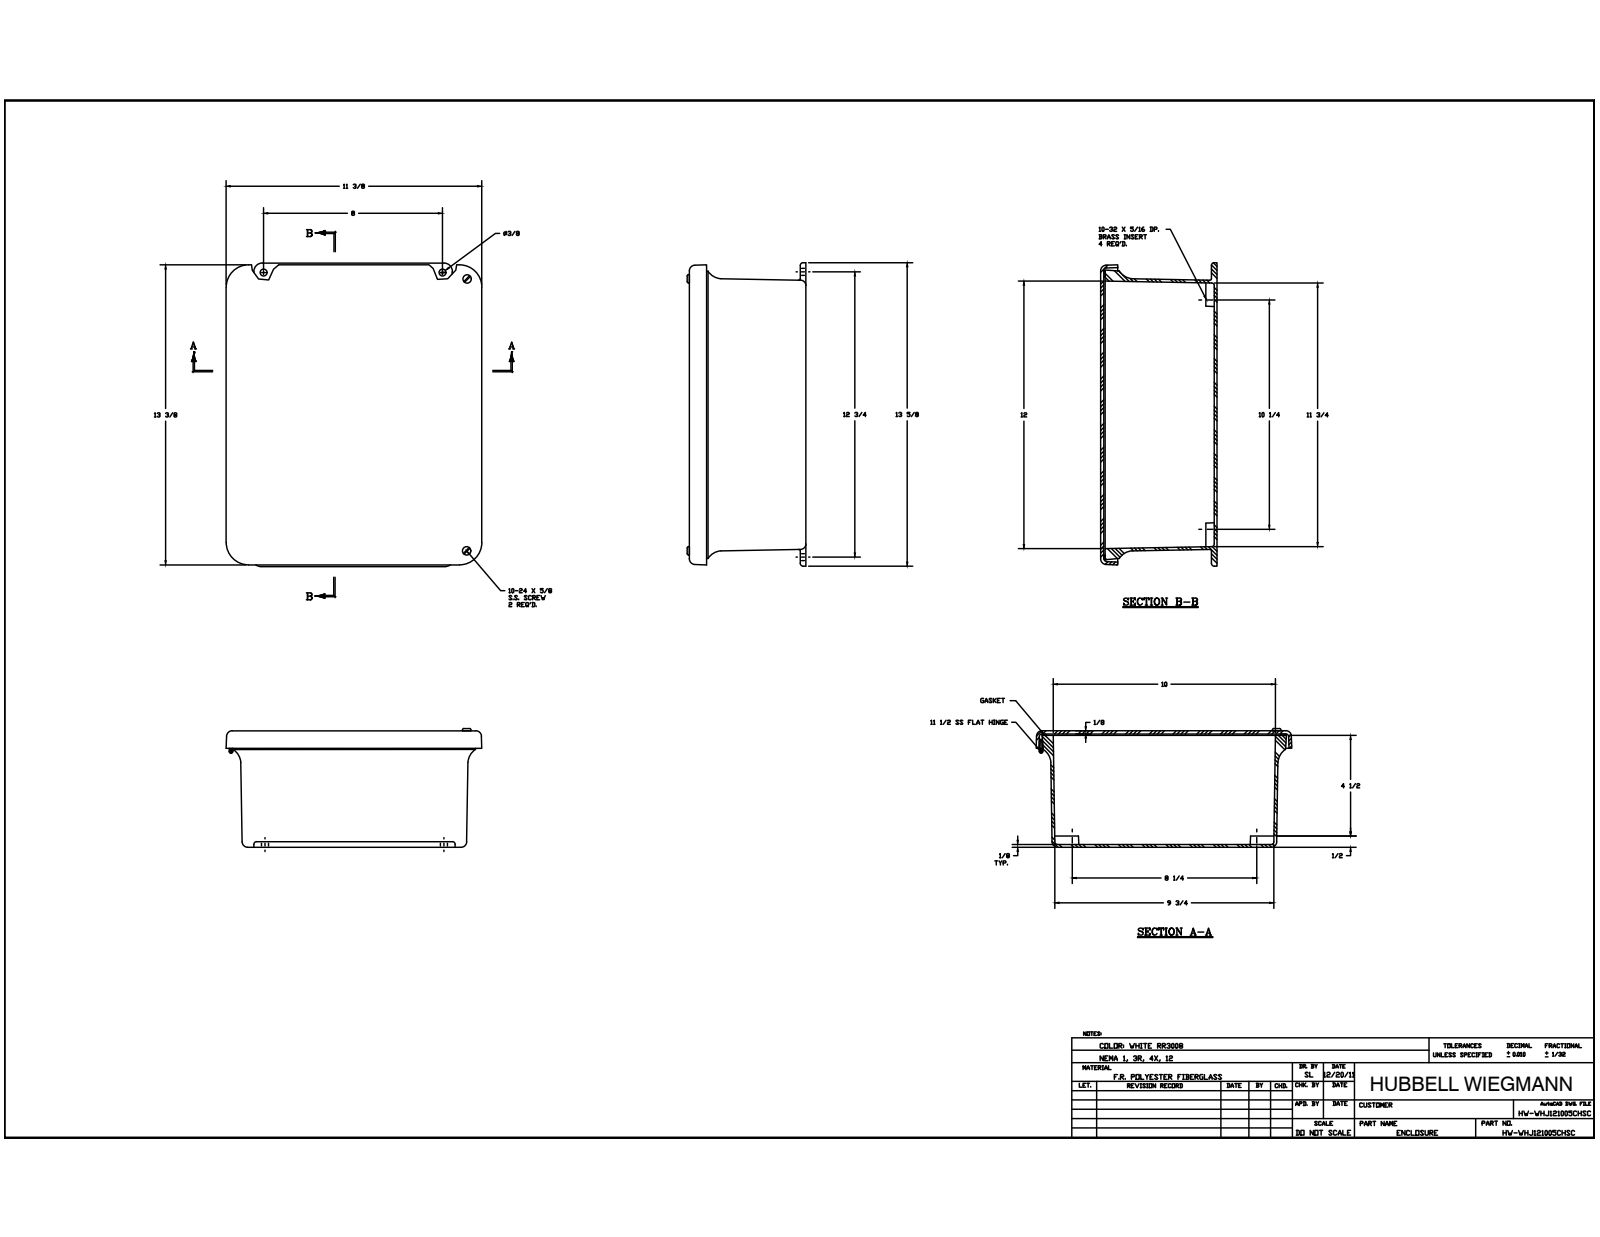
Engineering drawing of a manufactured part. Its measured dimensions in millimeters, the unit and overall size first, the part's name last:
Units: millimetres
Overall size (bounding box): 344.49 × 291.05 × 136.19
Round holes (diameter × count): ⌀3.33 ×8, ⌀3.56 ×8, ⌀3.86 ×5, ⌀3.96 ×4, ⌀5.54 ×4, ⌀3.68 ×2, ⌀2.16 ×1, ⌀2.16 ×1
Round bosses / shafts (diameter × count): ⌀6.35 ×8, ⌀3.17 ×8, ⌀6.86 ×6, ⌀4.83 ×2, ⌀3.97 ×2, ⌀3.94 ×1
Partial cylindrical surfaces — rounded edges, fillets, slot ends (radius × count): R0.79 ×20, R3.17 ×12, R6.35 ×8, R5.08 ×4, R9.53 ×4, R19.05 ×4, R1.6 ×2
Main face-to-face distances: 3.63, 3.18, 129.23, 132.86, 126.05, 129.68, 127, 5.86, 123.82, 2.23
Hole centre spacings: 92.08, 34.24, 235, 285.58, 368.25, 6.35, 92.07, 174.62
Volume: 1 419 000 mm³ · Surface area: 752 192 mm²
Bodies: 22 solids, 791 faces (283 planar, 303 cylindrical, 205 other)
Part name (STEP PRODUCT): J1210HW_1; RMINS45821P_113; RMINS45821P_114; RMINS45821P_115 (+8 more)
STEP written by: Autodesk Inventor 2014 (AUTOMOTIVE_DESIGN)
